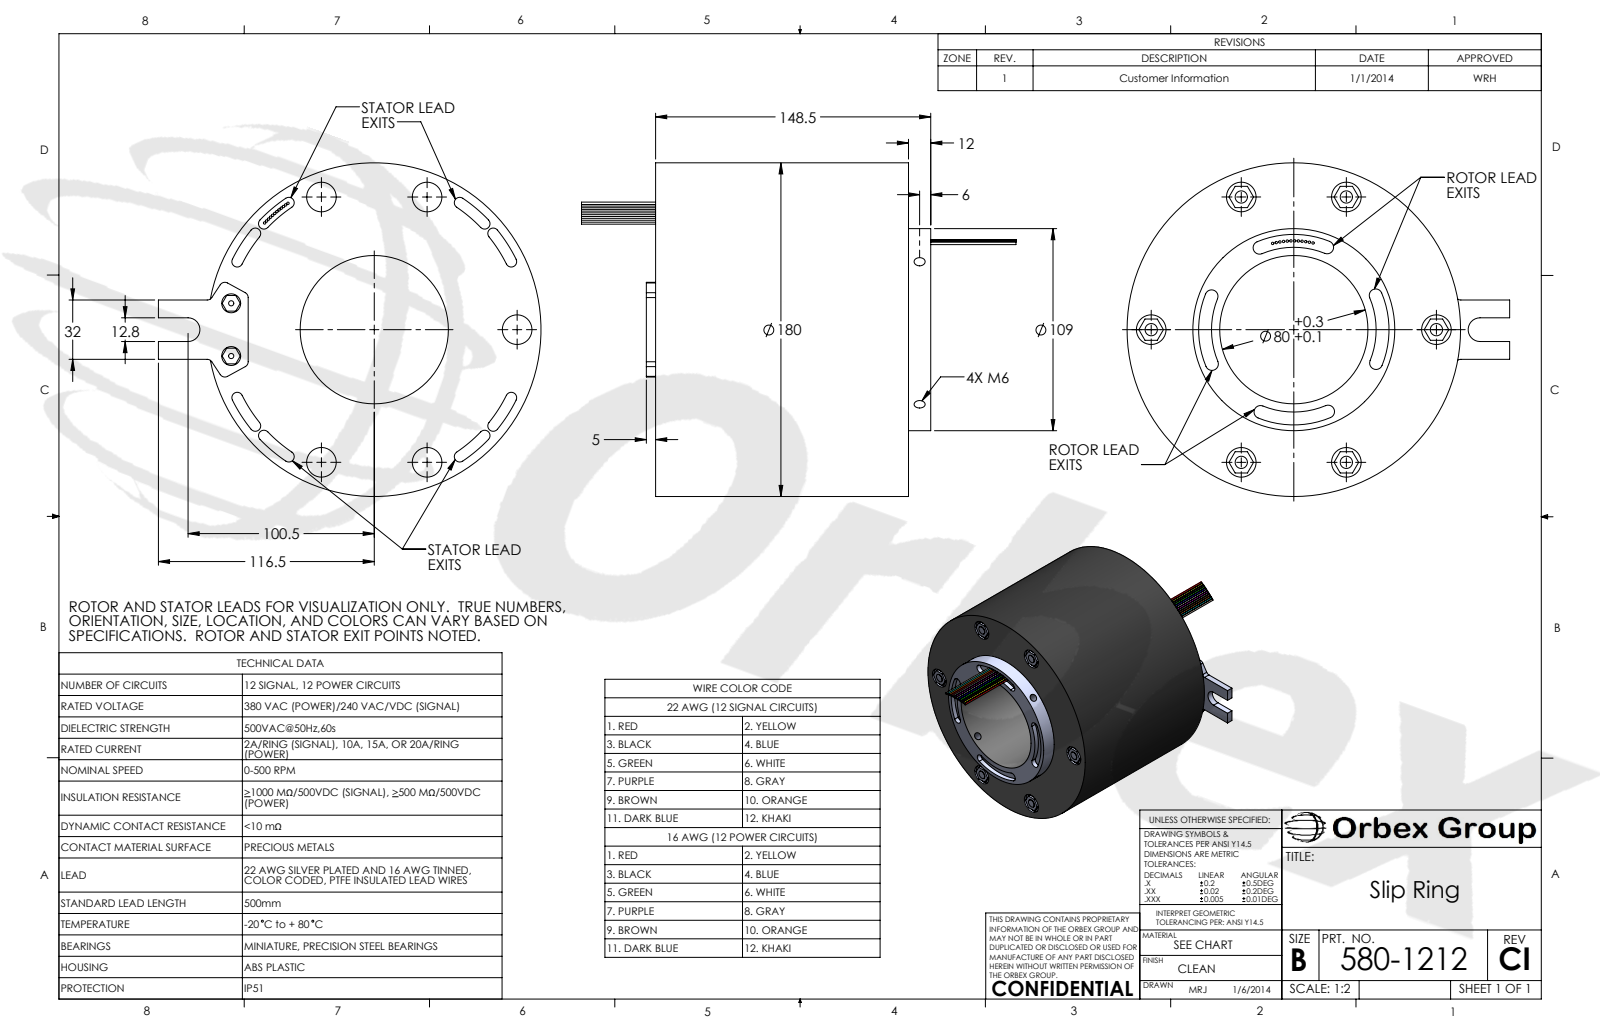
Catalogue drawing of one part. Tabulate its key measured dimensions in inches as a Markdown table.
| quantity | value |
| --- | --- |
| part name | 580-1212 Rev CI |
| STEP written by | SolidWorks 2013 (CONFIG_CONTROL_DESIGN) |
| units | inches |
| bodies | 1 solid, 306 faces (131 planar, 175 cylindrical, 0 other) |
| overall size | 9.232 × 8.13 × 7.087 |
| volume | 172.9 in³ |
| surface area | 268.3 in² |
| round holes (diameter × count) | 0.63 × 12, 0.236 × 4, 0.111 × 2, 0.403 × 2, 3.15 × 1 |
| round bosses / shafts (diameter × count) | 0.051 × 24, 0.261 × 6, 7.087 × 1, 4.291 × 1 |
| partial cylindrical surfaces (radius × count) | 0.115 × 16, 0.137 × 8, 0.118 × 6, 0.252 × 1, 1.749 × 1, 2.023 × 1, 3.135 × 1, 3.365 × 1 |
| main face-to-face distances | 5.374, 5.846, 0.472, 0.079, 0.157, 5.689, 5.295, 5.217, 0.197, 5.571 |
| hole center spacings | 5.019, 0.56, 2.239, 3.031, 3.032, 3.402, 3.405, 3.406 |
